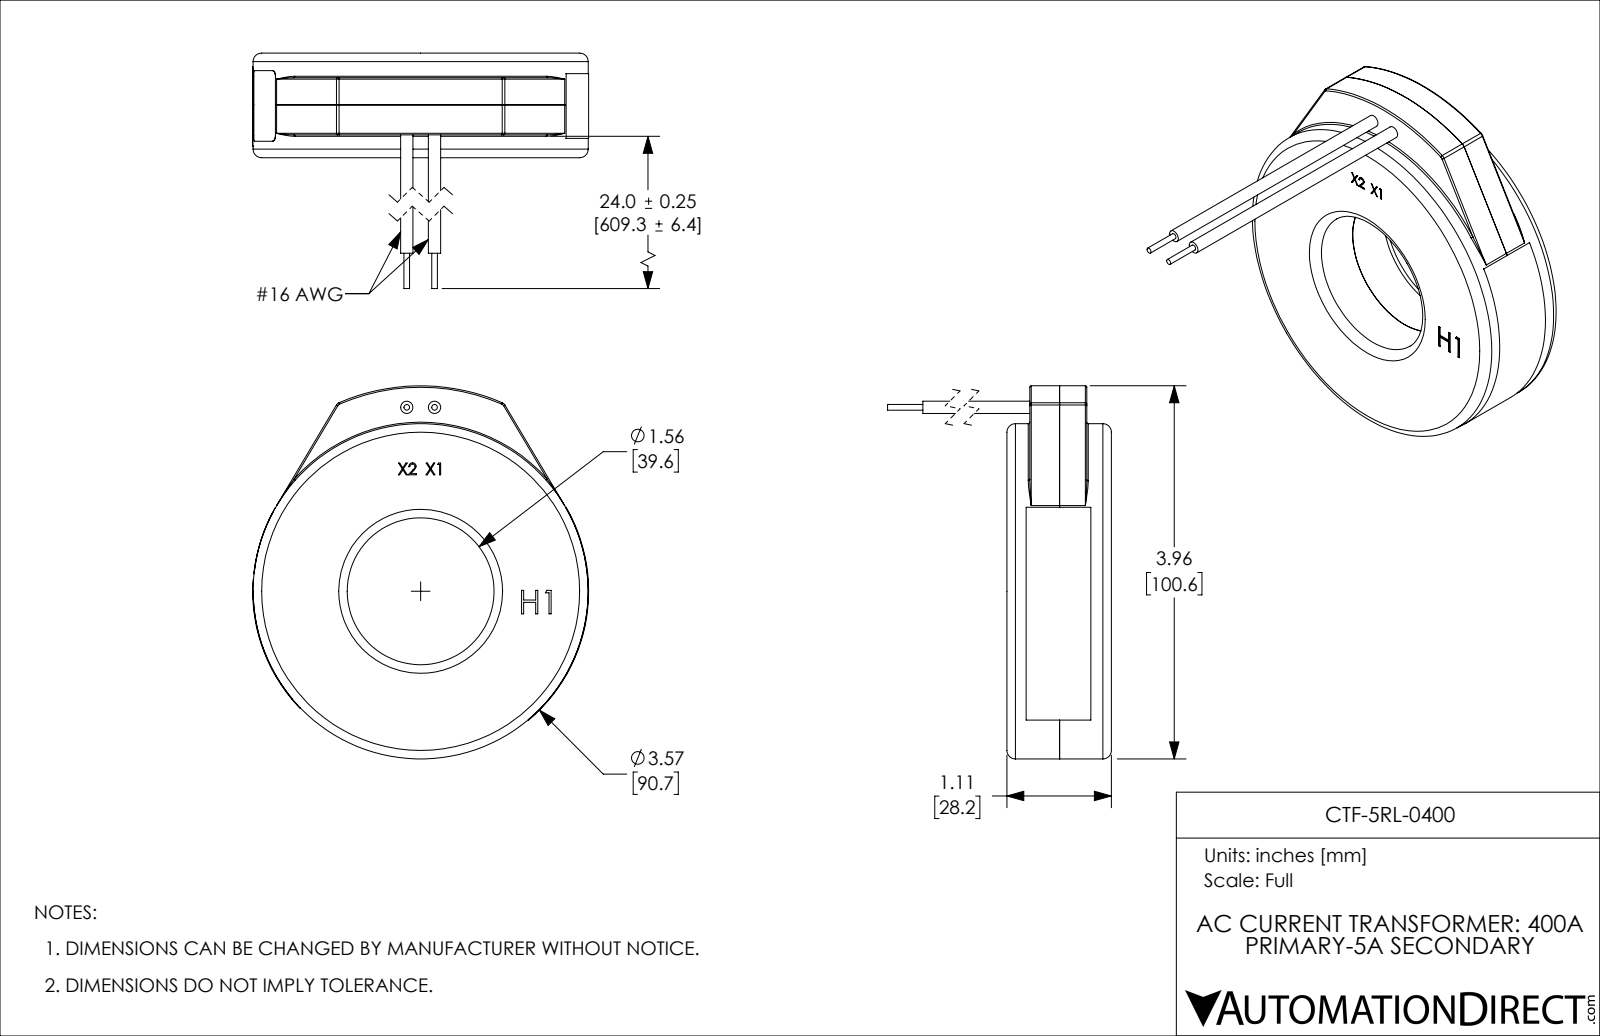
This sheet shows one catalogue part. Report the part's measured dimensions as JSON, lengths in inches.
{"part_name": "CTF-5RL-0400", "step_written_by": "SolidWorks 2018 (AUTOMOTIVE_DESIGN)", "units": "inches", "bodies": {"solids": 7, "faces": 154, "planar": 87, "cylindrical": 37, "other": 30}, "overall_size": [4.242, 3.962, 3.57], "volume_in3": 9.55, "surface_area_in2": 62.68, "round_holes": [[1.56, 1]], "round_bosses_or_shafts": [[0.13, 2], [0.06, 2], [3.56, 1]], "partial_cylinders_radius": [[0.125, 3], [0.015, 2], [0.016, 2], [0.06, 2], [1.779, 1], [1.782, 1], [1.785, 1], [2.182, 1]], "face_to_face_distances": [0.55, 1.11, 0.56, 0.867, 0.317, 0.243, 0.261, 0.289, 0.606, 0.849]}
